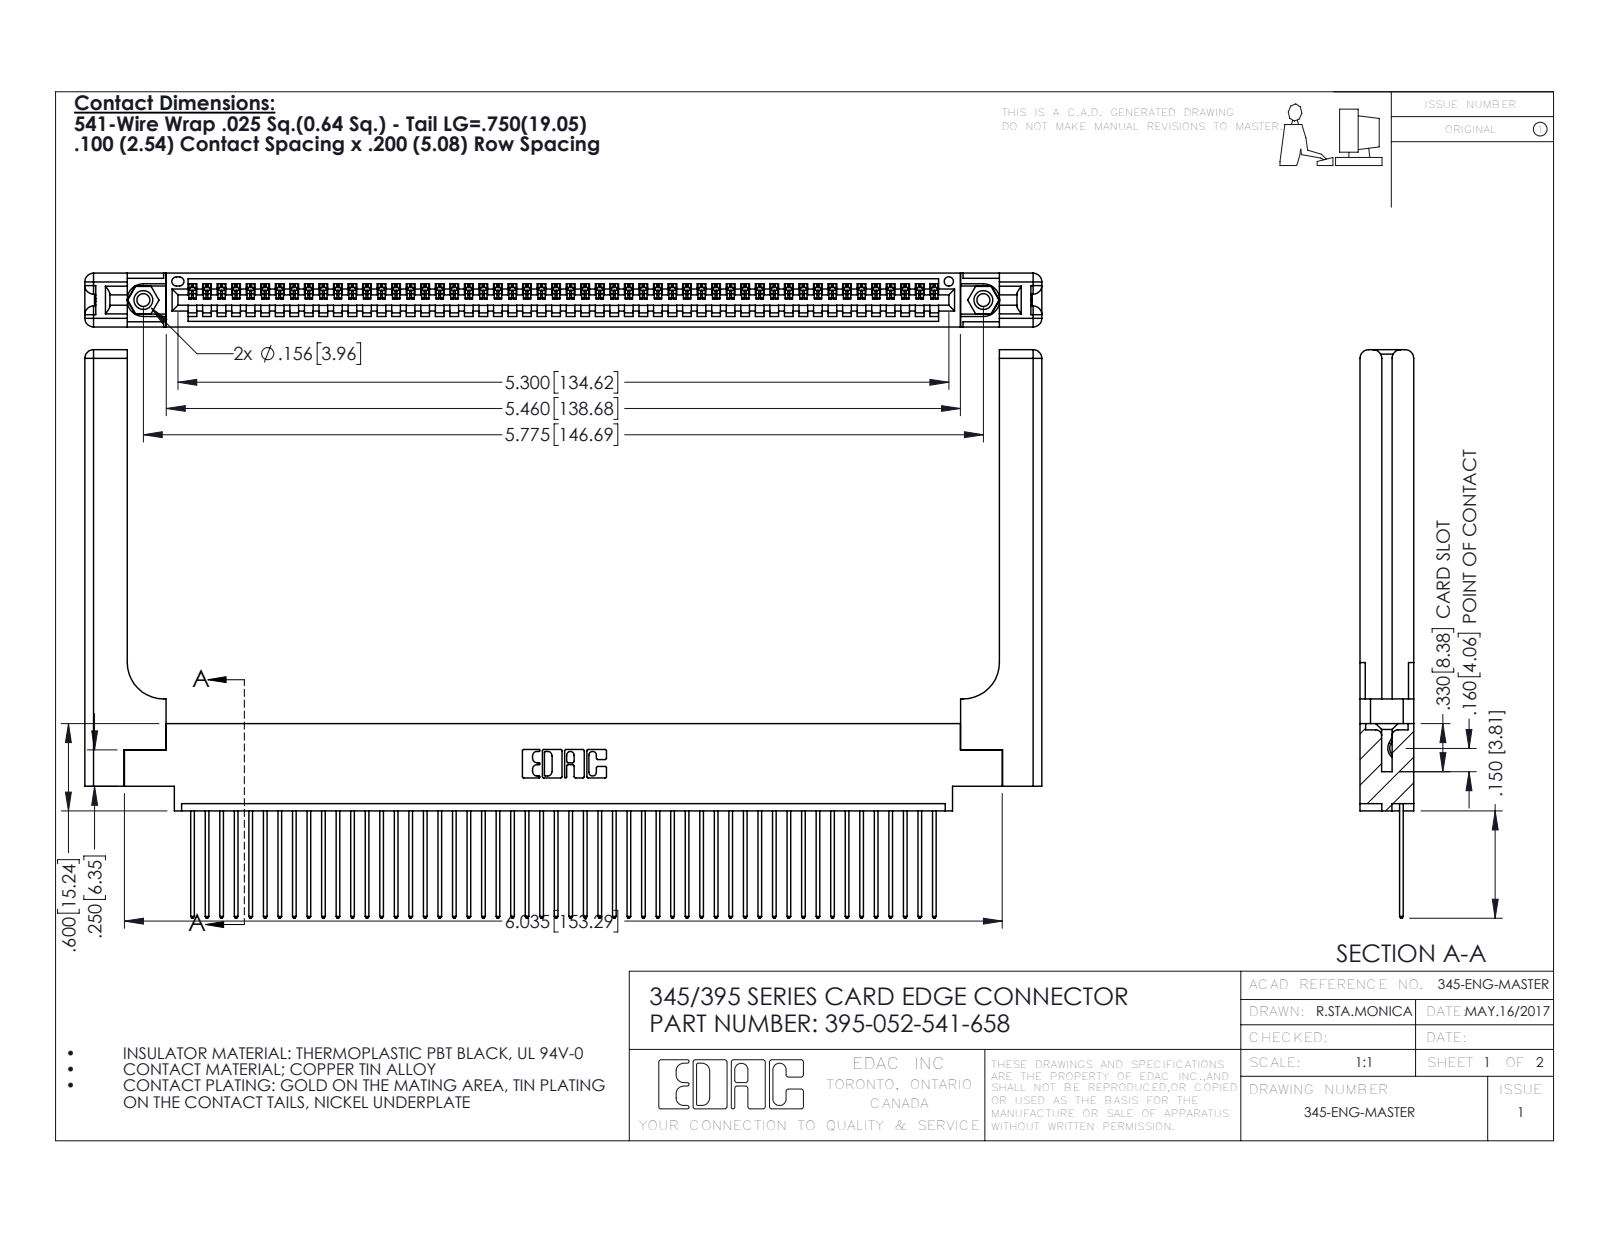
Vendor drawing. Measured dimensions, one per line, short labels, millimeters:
name: 345-220-058_345-220-058; 345-250-001_345-250-001-102; 395-052-541-658; 345-292-001_345-293-141 (+1 more)
written by: SolidWorks 2016 (CONFIG_CONTROL_DESIGN)
unit: mm
bodies: 57 solids, 3402 faces (2312 planar, 1030 cylindrical, 60 other)
size: 167.1 × 99.2 × 9.4
volume: 24 520 mm³; area: 27 860 mm²
holes: 2× ⌀2.3, 2× ⌀3.2, 2× ⌀4, 1× ⌀1.6
bosses: 2× ⌀3.9
rounds: 104× R0.2, 104× R0.3, 22× R0.3, 16× R1.5, 6× R0.2, 6× R0.8, 3× R0.7, 2× R0.8
face distances: 1.8, 7.6, 9.4, 2.5, 6.9, 0.6, 5.1, 5.7, 3.8, 3.8
hole spacings: 6.9, 140.7, 146.7
